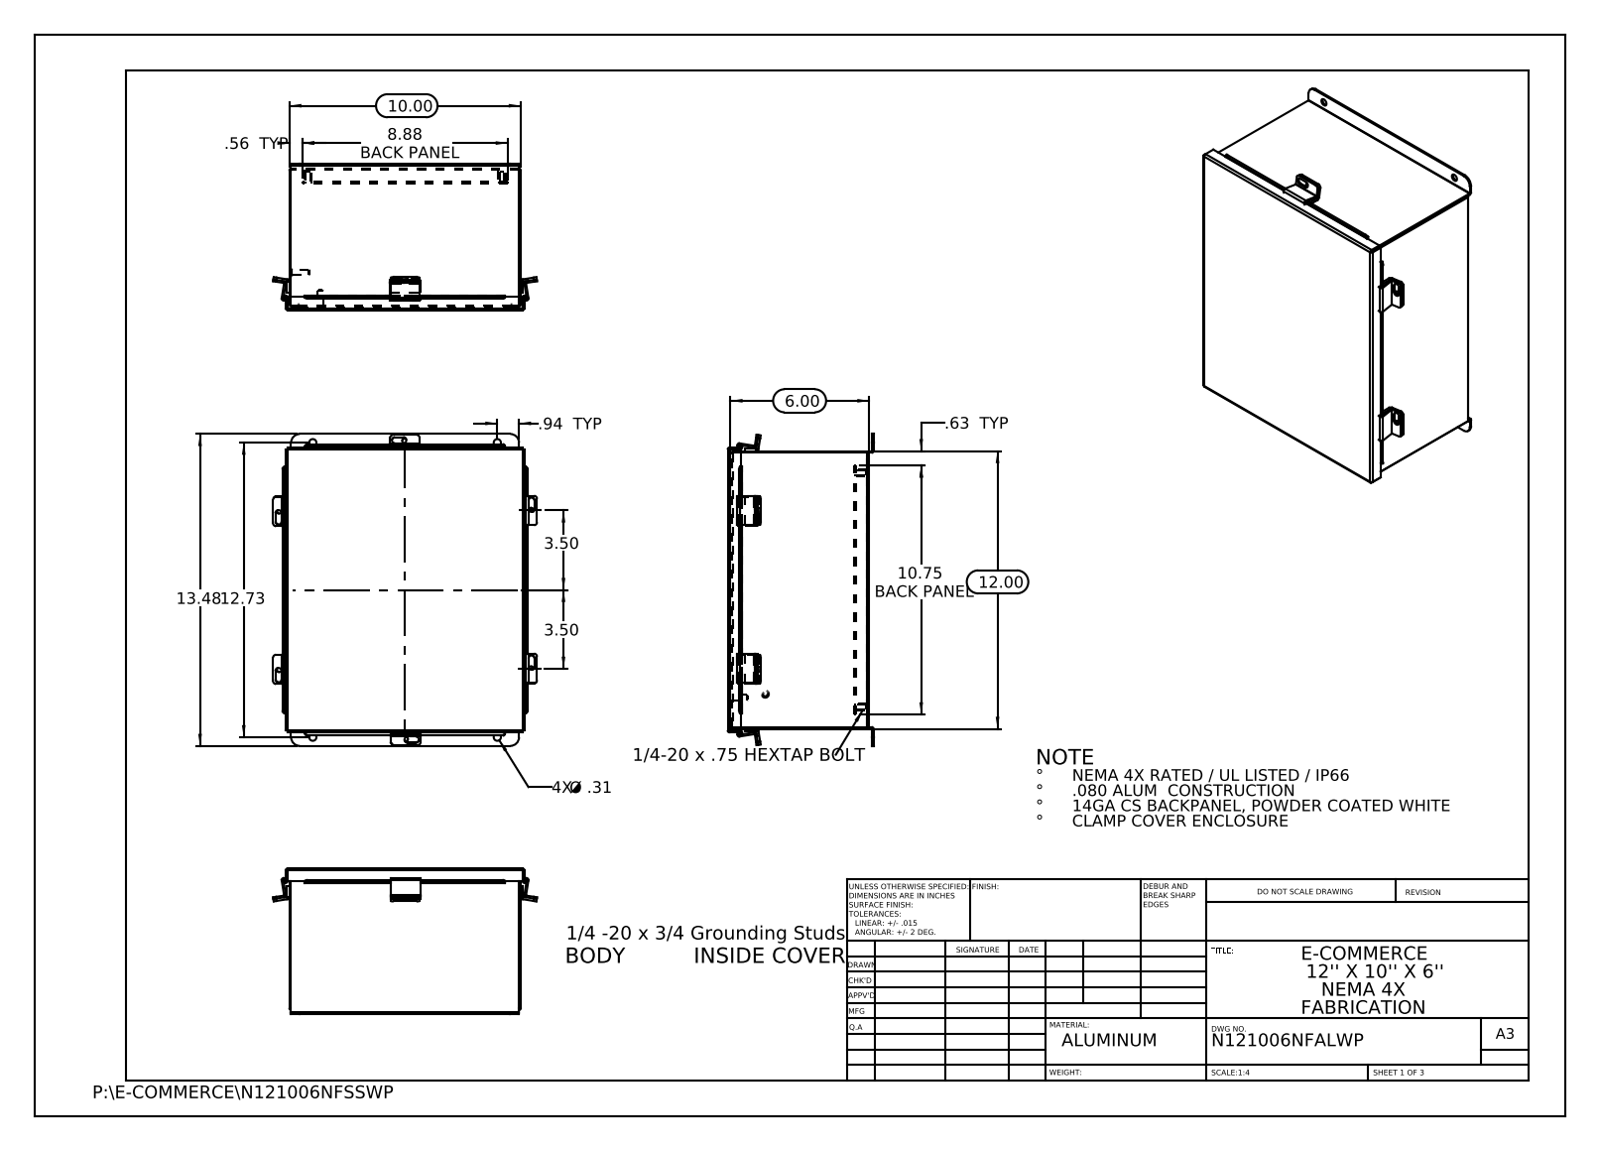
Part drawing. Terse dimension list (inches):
name: N121006NFSSWP JIC Cover Clamp; N121006NFSSWP JIC Backpanel; N121006NFSSWP JIC Enclosure Template; N121006NFSSWP JIC Bottom (+6 more)
written by: SolidWorks 2013 (CONFIG_CONTROL_DESIGN)
unit: in
bodies: 23 solids, 548 faces (356 planar, 172 cylindrical, 20 other)
size: 13.476 × 11.407 × 6.39
volume: 50.74 in³; area: 1 376 in²
holes: 10× ⌀0.25, 4× ⌀0.187, 4× ⌀0.312
bosses: 4× ⌀0.313, 2× ⌀0.315, 2× ⌀0.236
rounds: 21× R0.125, 16× R0.009, 12× R0.013, 12× R0.088, 12× R0.133, 8× R0.083, 8× R0.1, 4× R0.084
face distances: 0.075, 6.128, 9.925, 11.925, 6.053, 6.203, 0.074, 0.575, 0.5, 5.553
hole spacings: 1.315, 8.278, 11.428, 14.05, 6.85, 7.976, 8.375, 10.126
